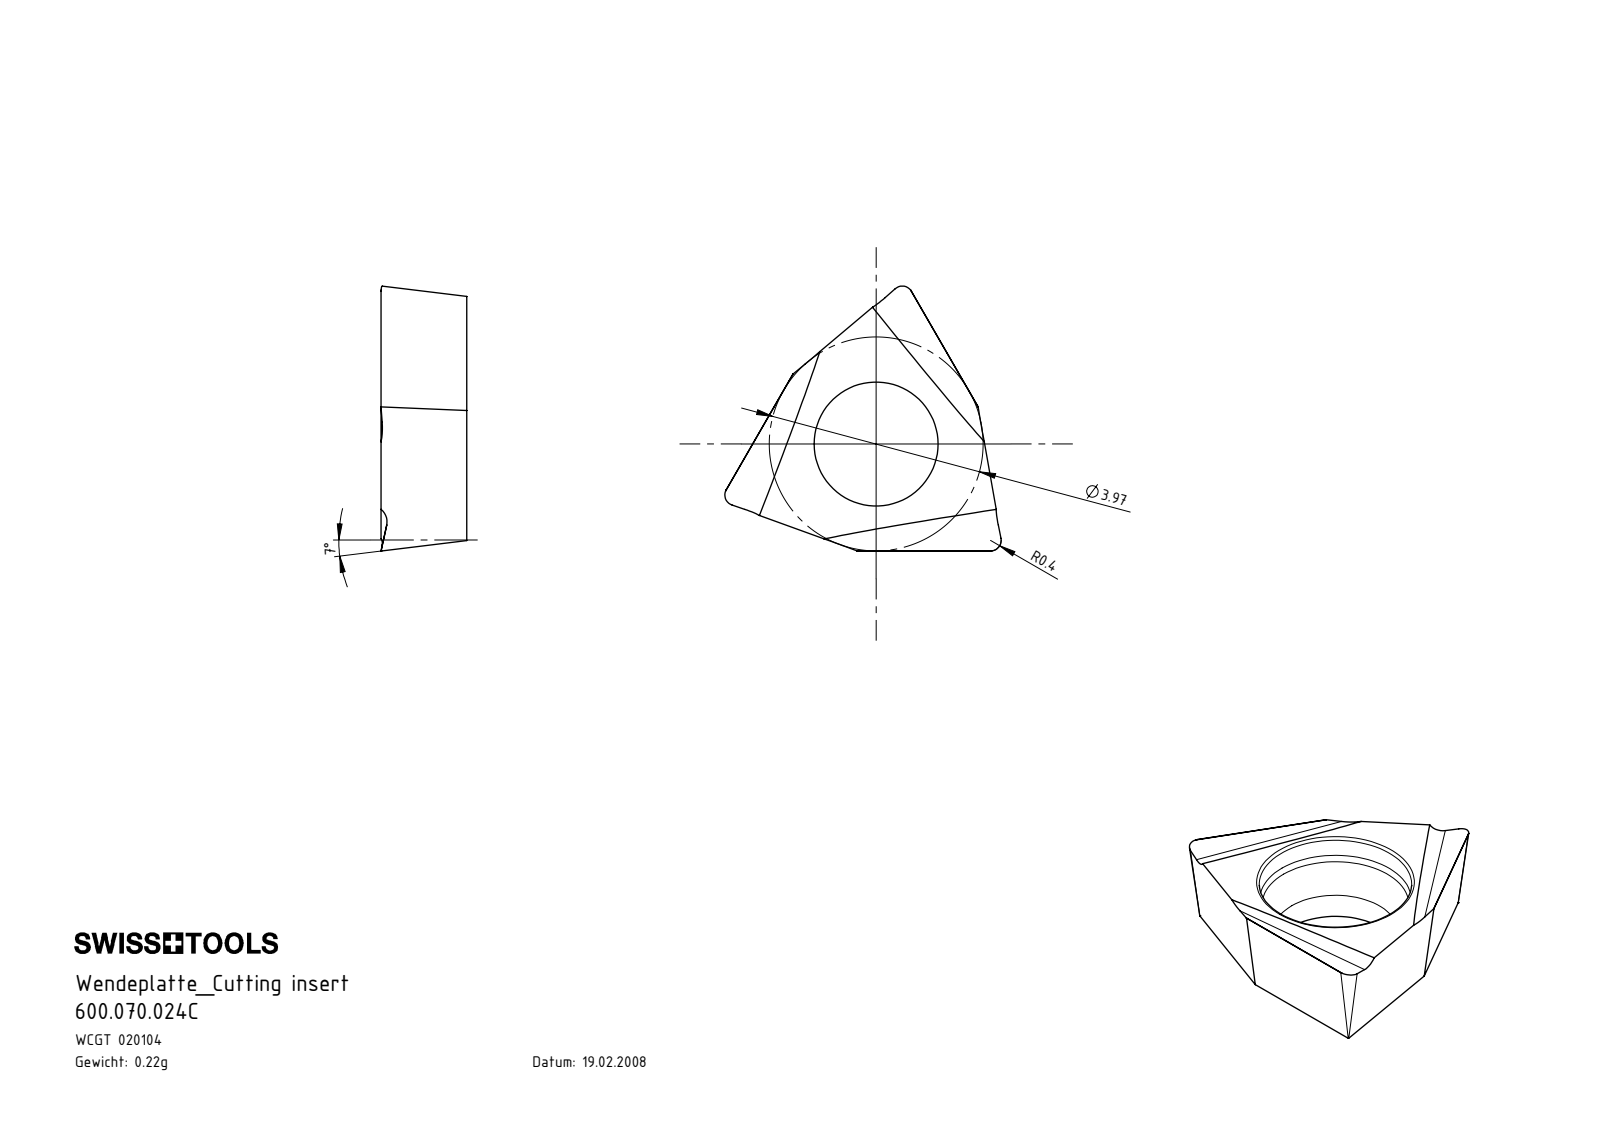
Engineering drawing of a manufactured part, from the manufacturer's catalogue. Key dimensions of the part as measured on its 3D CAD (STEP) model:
Part name (STEP PRODUCT): 600.070.024C
STEP written by: SolidWorks 2022 (AUTOMOTIVE_DESIGN)
Units: millimetres
Bodies: 1 solid, 31 faces (14 planar, 5 cylindrical, 12 other)
Overall size (bounding box): 5.13 × 4.92 × 1.59
Volume: 15 mm³ · Surface area: 56 mm²
Round holes (diameter × count): ⌀2.3 ×1
Partial cylindrical surfaces — rounded edges, fillets, slot ends (radius × count): R0.3 ×3
Main face-to-face distances: 1.59
